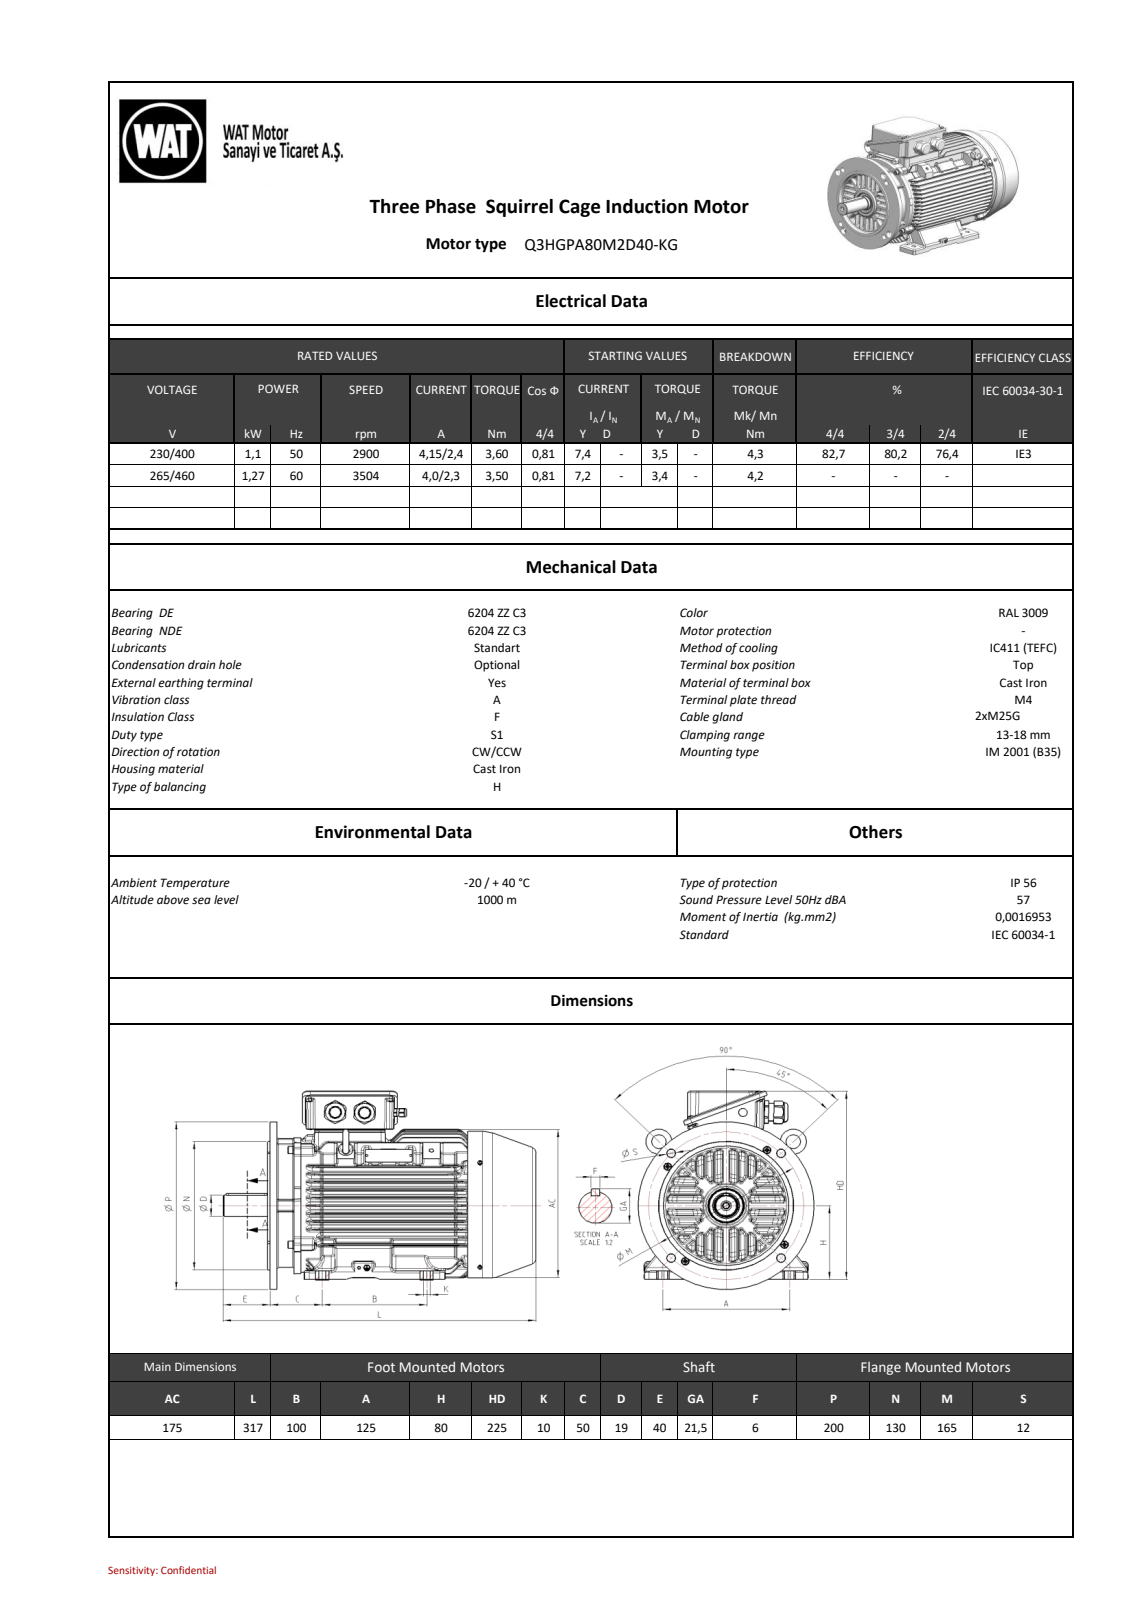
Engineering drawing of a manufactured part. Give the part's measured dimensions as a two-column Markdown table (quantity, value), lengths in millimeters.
| quantity | value |
| --- | --- |
| part name | 26000A30F4D8ro9c |
| STEP written by | SIEMENS PLM Software NX 11.0 (AUTOMOTIVE_DESIGN) |
| units | millimeters |
| bodies | 0 solids, 2941 faces (783 planar, 816 cylindrical, 1342 other) |
| overall size | 316.71 × 244.98 × 221.33 |
| round holes (diameter × count) | 10 × 6, 12 × 4, 2.5 × 2, 3.3 × 2, 17.2 × 2, 4 × 1, 6.4 × 1, 6.5 × 1, 27.8 × 1, 168 × 1 |
| round bosses / shafts (diameter × count) | 20 × 4, 8.65 × 3, 8 × 3, 5 × 3, 27.7 × 2, 25.25 × 2, 8.5 × 2, 200 × 1 |
| partial cylindrical surfaces (radius × count) | 1.5 × 302, 2 × 54, 2.5 × 46, 1 × 28, 4 × 24, 5 × 22, 7 × 13, 3 × 12 |
| main face-to-face distances | 4.95, 229.98, 234.93, 41.78, 271.76, 276.71, 62.56, 3.01, 1.5, 152.95 |
| hole center spacings | 116.67, 133.37, 21.53, 61.25, 77, 82.5, 97.19, 126.58 |
